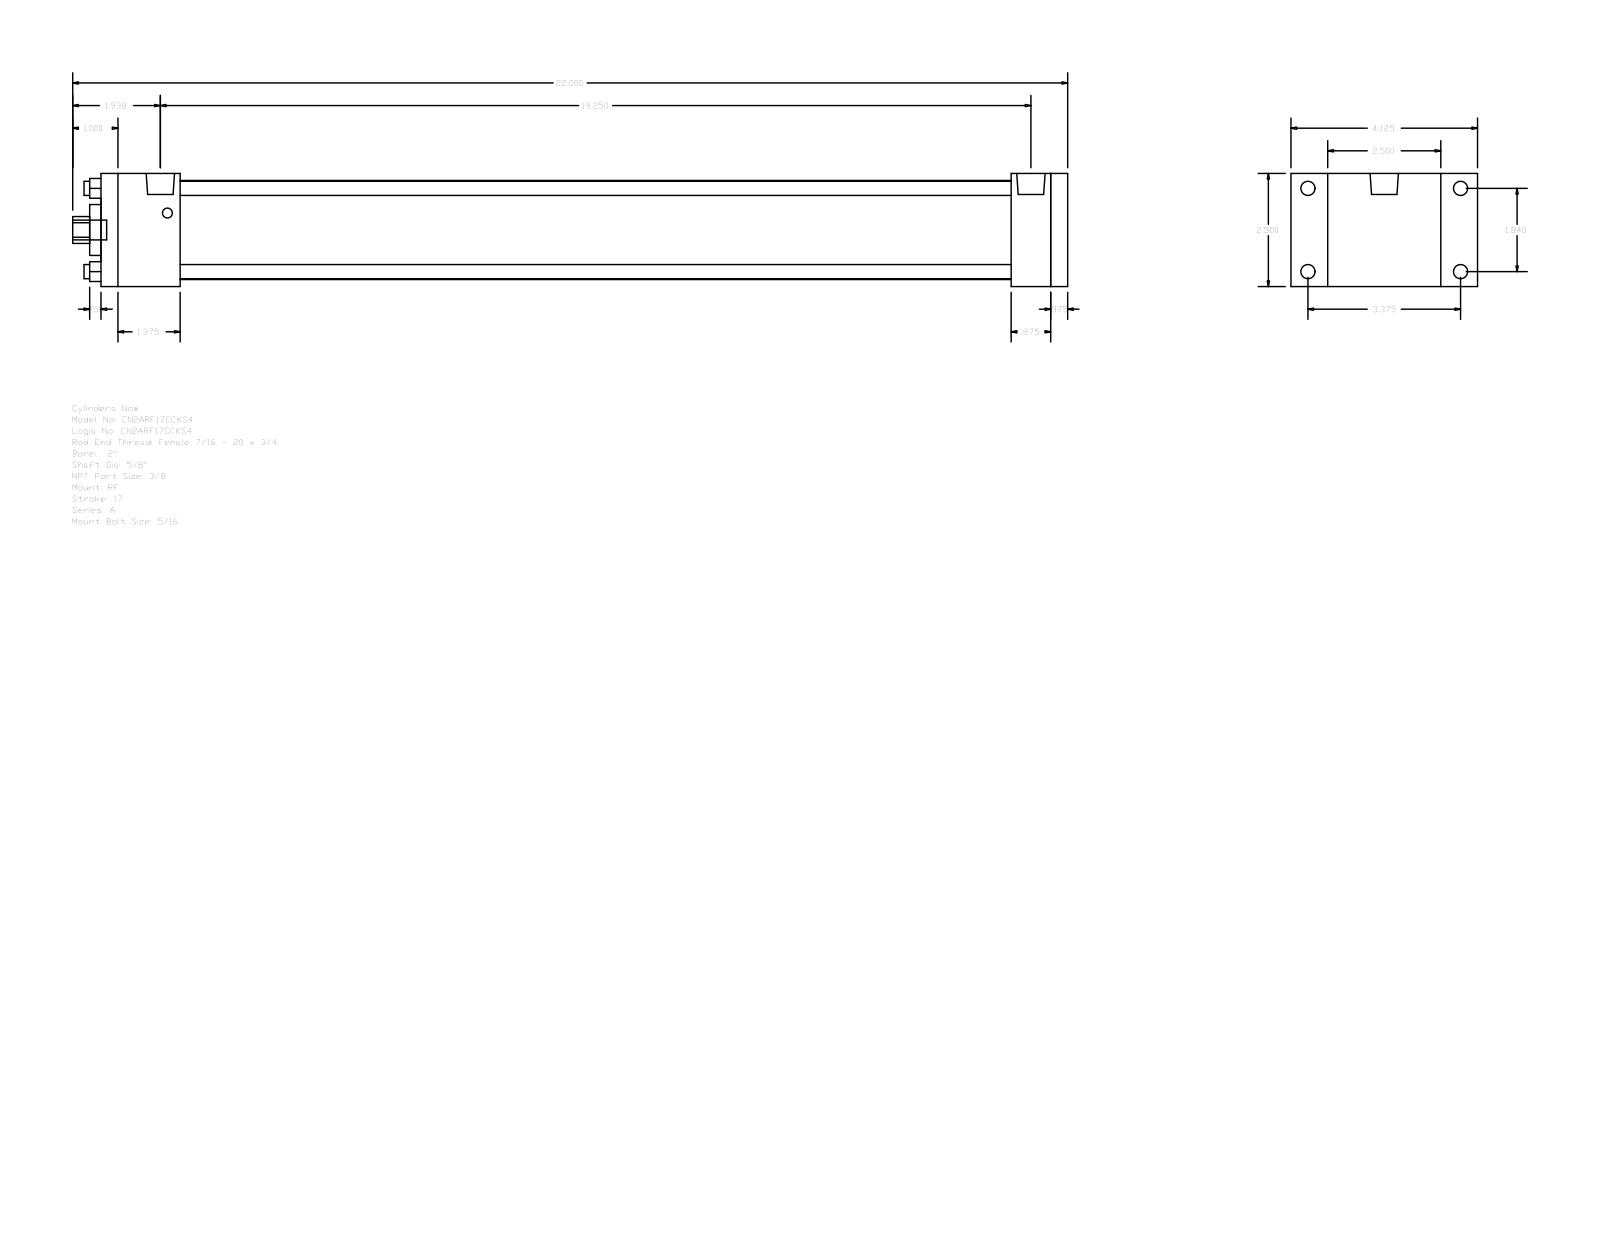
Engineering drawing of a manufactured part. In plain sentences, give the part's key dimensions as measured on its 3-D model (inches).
The part is named "A_RF__0200_0.625". Its 3-D file was written by "GSSL Pune (CONFIG_CONTROL_DESIGN)". It is 0 solids with 92 faces: 64 planar, 28 cylindrical and 0 other. Overall it measures 22 by 4.125 by 2.5 inches. Round holes: 4 of diameter 0.313, 1 of diameter 0.625, 1 of diameter 1.125, 1 of diameter 2.19. Round bosses or shafts: 4 of diameter 0.313, 4 of diameter 0.219, 2 of diameter 0.627, 1 of diameter 0.437. Partial cylindrical surfaces (rounded edges, fillets, slot ends): 1 of radius 0.297. The main face-to-face distances are 2.5, 21.375, 0.375, 21, 1.75, 19.25, 19.625, 20.125, 18.375, 0.875. The hole center spacings are 1.301, 1.84, 2.602.
